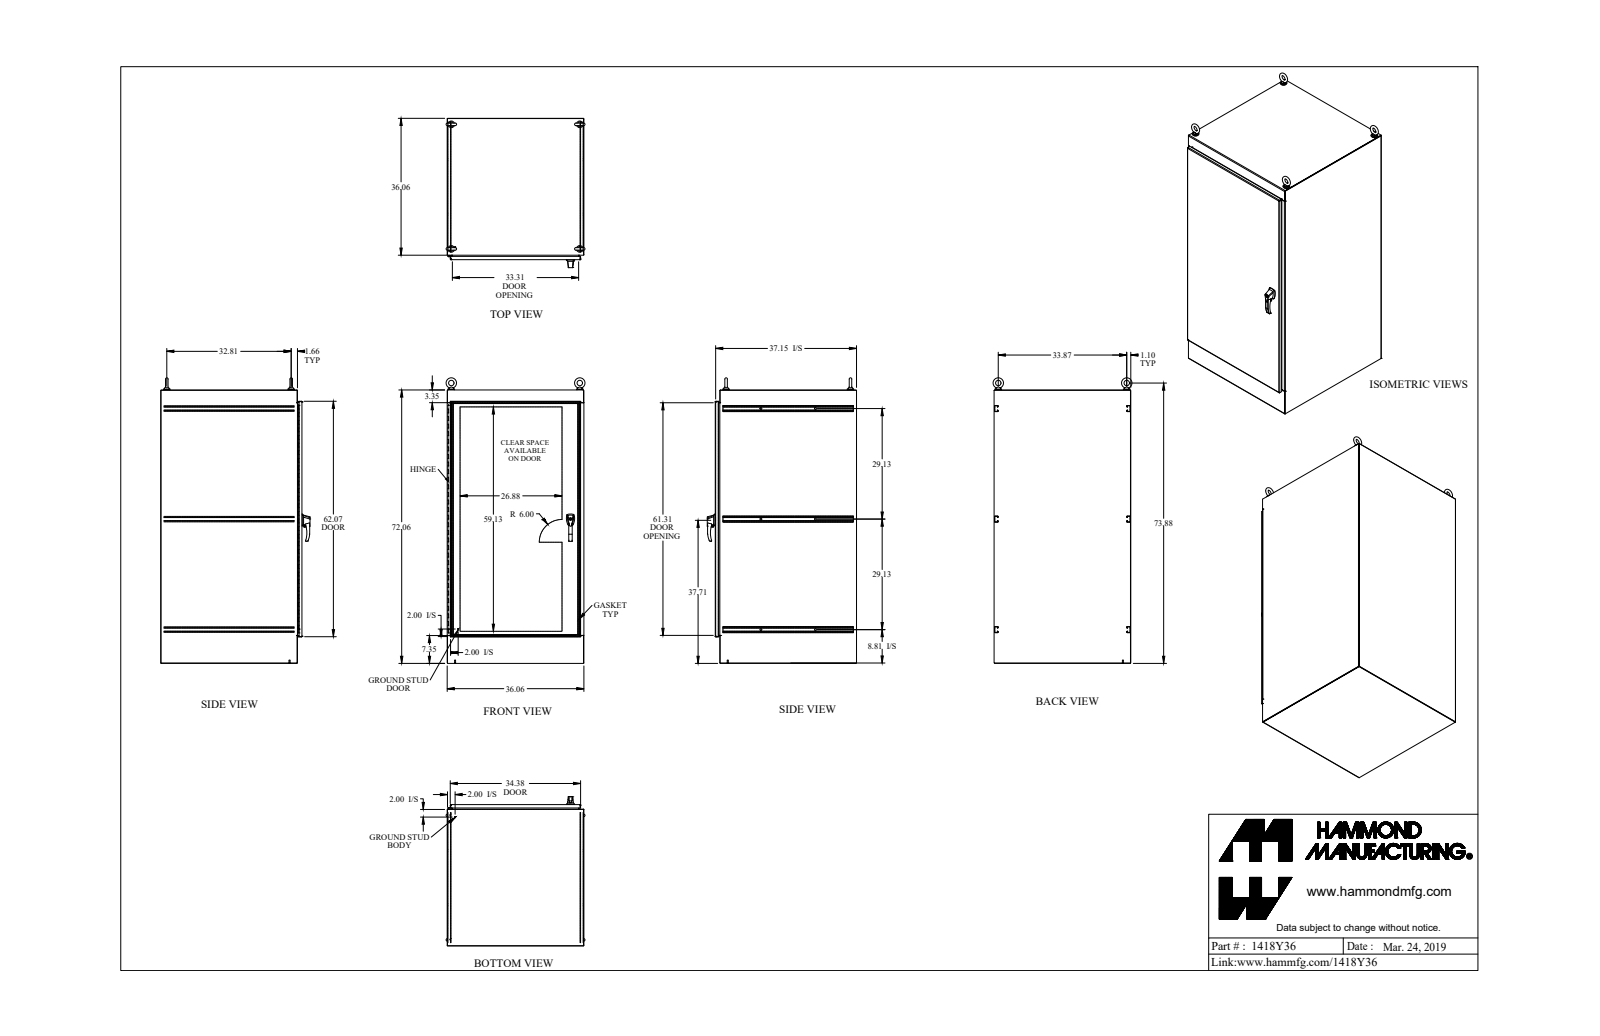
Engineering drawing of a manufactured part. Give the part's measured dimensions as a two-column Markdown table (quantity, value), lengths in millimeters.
| quantity | value |
| --- | --- |
| part name | 1418Y36_Default |
| STEP written by | SolidWorks 2019 (CONFIG_CONTROL_DESIGN) |
| units | millimeters |
| bodies | 61 solids, 1880 faces (813 planar, 842 cylindrical, 225 other) |
| overall size | 1923.1 × 999.8 × 942.8 |
| volume | 23 810 000 mm³ |
| surface area | 19 660 000 mm² |
| round holes (diameter × count) | 7.7 × 10, 12.7 × 6, 13.4 × 4, 15.9 × 4, 17.4 × 4, 19.1 × 4, 6.4 × 2, 6.5 × 2, 7.1 × 2, 7.1 × 2, 8 × 2, 9.9 × 2 |
| round bosses / shafts (diameter × count) | 44.5 × 4, 38.1 × 4, 31.8 × 4, 18.7 × 4, 7.1 × 4, 25.4 × 2, 19.1 × 2, 16 × 2 |
| partial cylindrical surfaces (radius × count) | 1.1 × 42, 3.5 × 36, 3.2 × 22, 0.5 × 16, 1.2 × 13, 3.6 × 13, 1.5 × 10, 0.4 × 8 |
| main face-to-face distances | 2.4, 913.5, 943.7, 911.1, 915.9, 1827.9, 941.2, 946.1, 1825.5, 1830.3 |
| hole center spacings | 152.4, 304.8, 457.2, 609.6, 762, 914.4, 365.1, 1066.8 |
